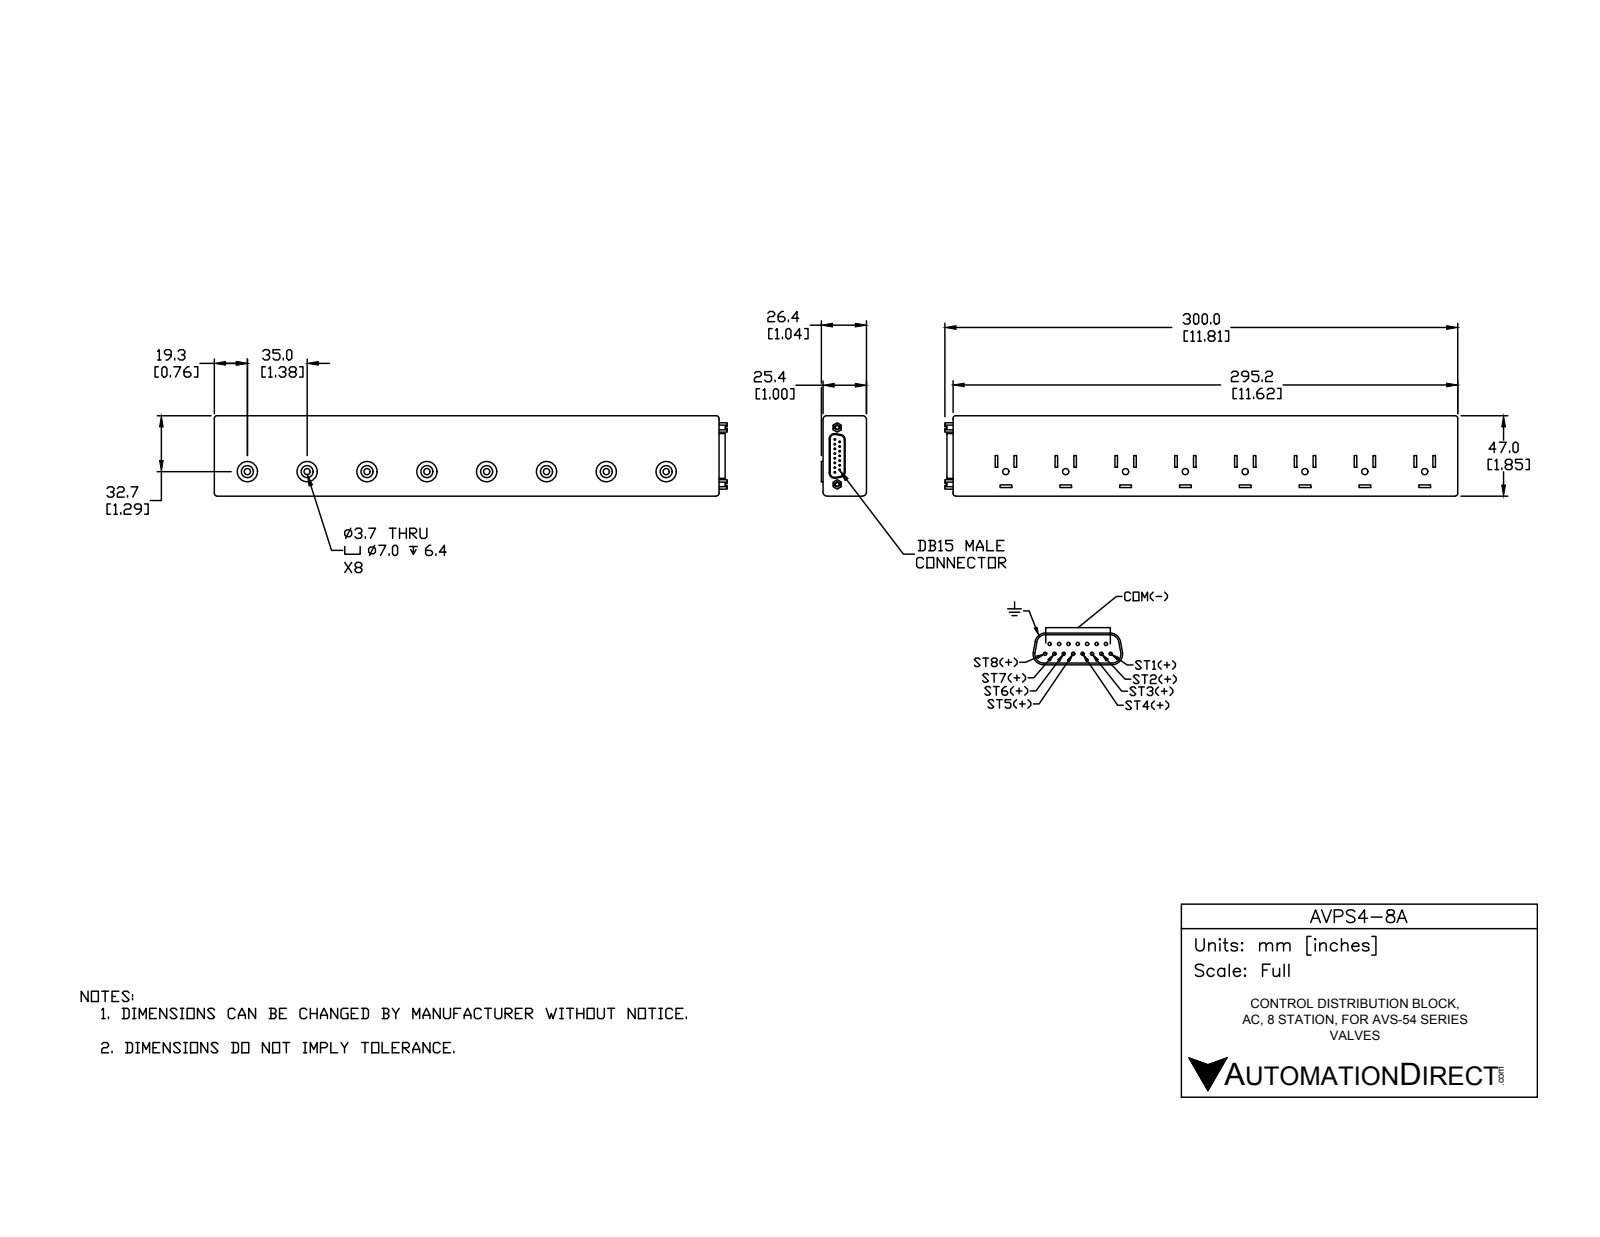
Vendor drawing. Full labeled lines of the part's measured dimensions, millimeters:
Part name (STEP PRODUCT): AVPS4-8A
STEP written by: SolidWorks 2016 (AUTOMOTIVE_DESIGN)
Units: millimetres
Bodies: 1 solid, 311 faces (195 planar, 104 cylindrical, 12 other)
Overall size (bounding box): 300.1 × 47 × 26.4
Volume: 346 300 mm³ · Surface area: 50 550 mm²
Round holes (diameter × count): ⌀3.7 ×8, ⌀7 ×8, ⌀2.3 ×2
Round bosses / shafts (diameter × count): ⌀1 ×15, ⌀11.9 ×8
Partial cylindrical surfaces — rounded edges, fillets, slot ends (radius × count): R1.6 ×6, R2.3 ×4, R2.6 ×4, R3.1 ×4, R1.6 ×2
Main face-to-face distances: 25.4, 47, 295.2, 1, 26.4, 1.5, 35, 6.4, 20.1, 40.5
Hole centre spacings: 35, 70, 105, 140, 175, 70, 105, 210
